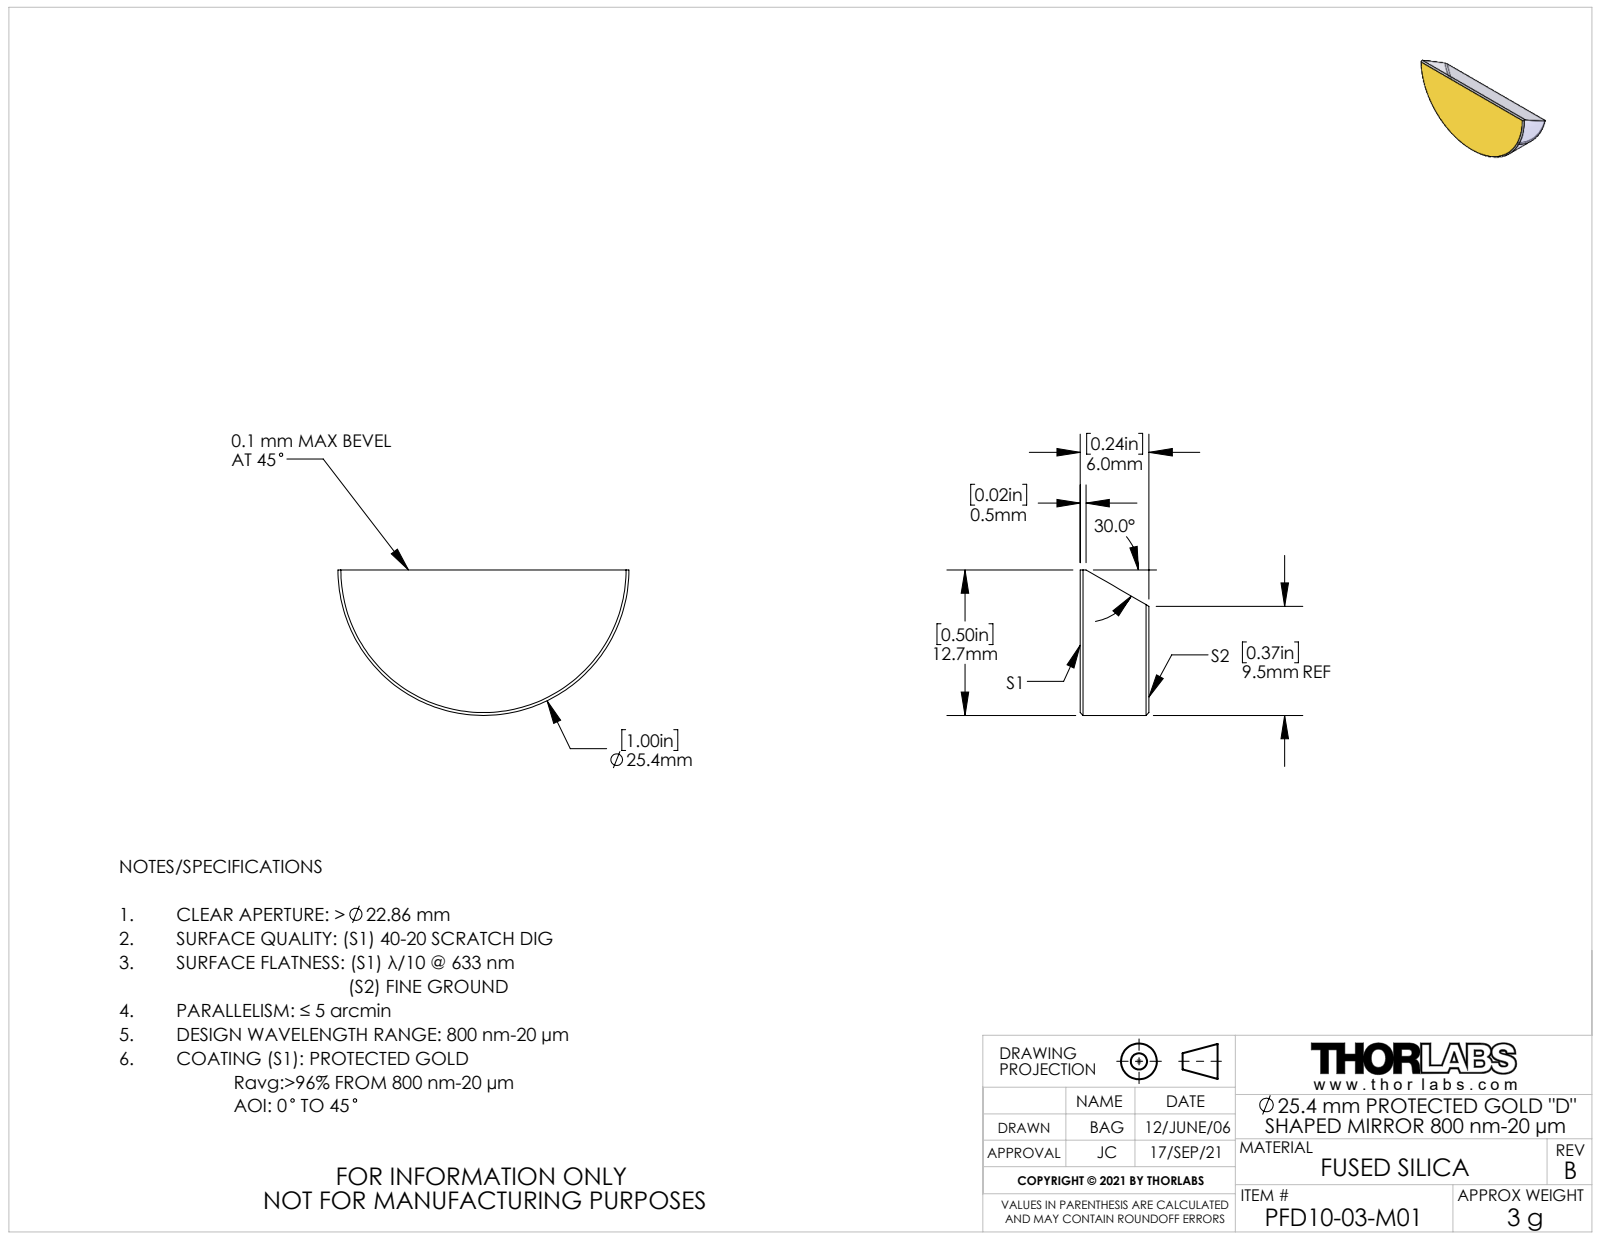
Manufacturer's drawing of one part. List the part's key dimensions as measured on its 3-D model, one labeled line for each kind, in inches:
Part name (STEP PRODUCT): 15655-E0W
STEP written by: SolidWorks 2007 (AUTOMOTIVE_DESIGN)
Units: inches
Bodies: 0 solids, 8 faces (5 planar, 1 cylindrical, 2 other)
Overall size (bounding box): 1 × 0.5 × 0.236
Partial cylindrical surfaces — rounded edges, fillets, slot ends (radius × count): R0.5 ×1
Main face-to-face distances: 0.236
